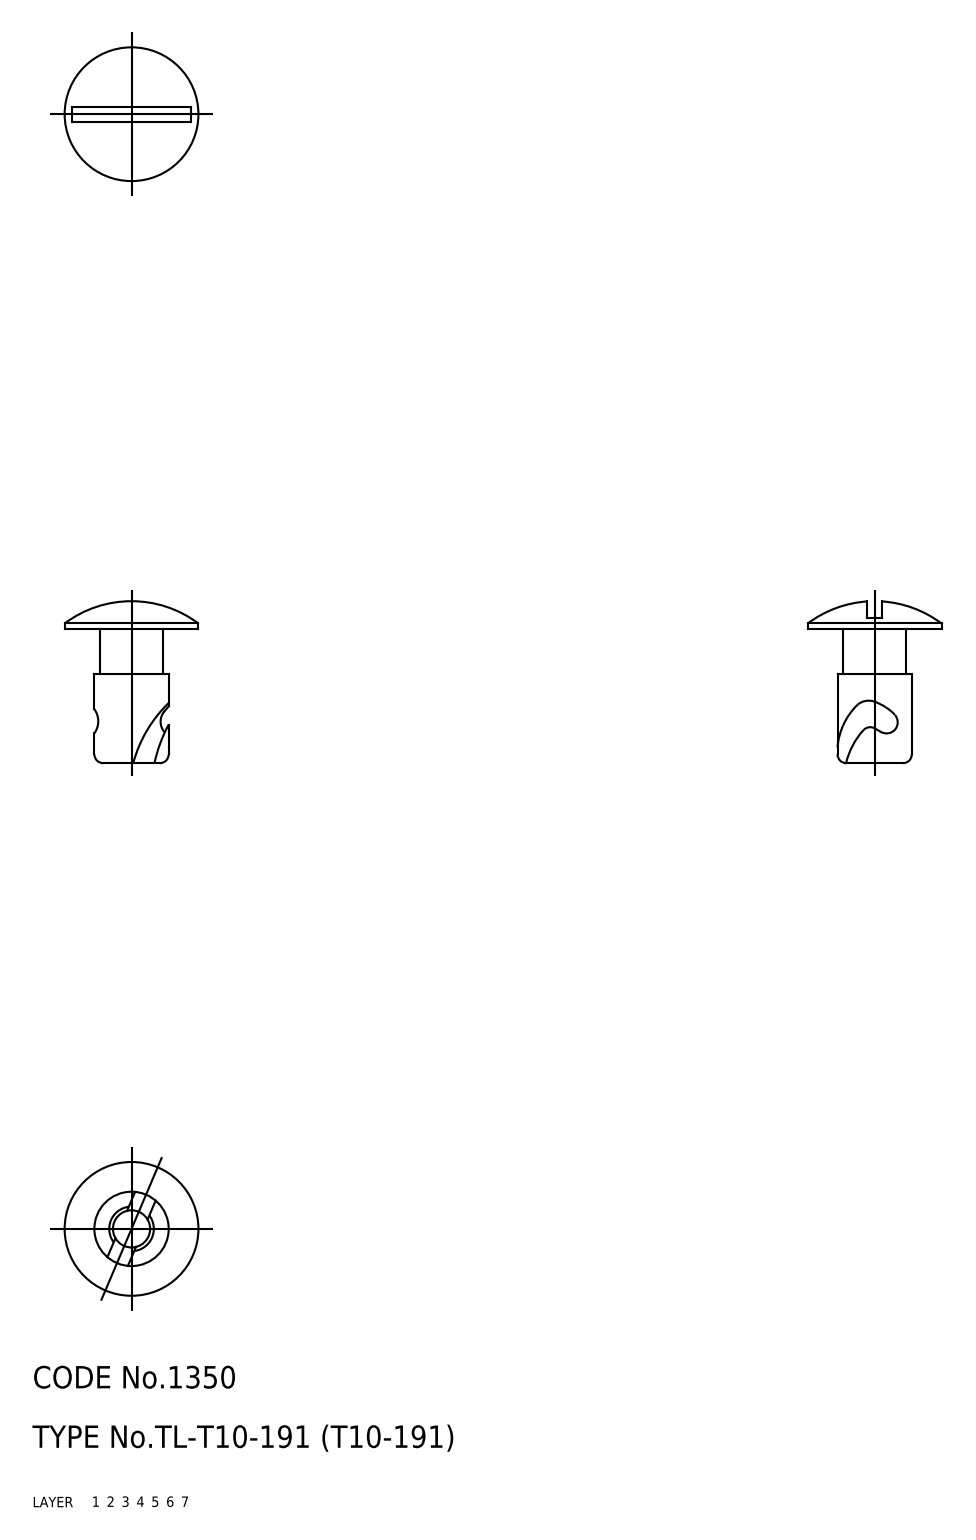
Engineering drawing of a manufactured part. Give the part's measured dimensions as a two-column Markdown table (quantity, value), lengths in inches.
| quantity | value |
| --- | --- |
| part name | fastener |
| STEP written by | CADfix (AUTOMOTIVE_DESIGN) |
| units | inches |
| bodies | 1 solid, 36 faces (0 planar, 0 cylindrical, 36 other) |
| overall size | 0.857 × 0.709 × 0.709 |
| volume | 0.091 in³ |
| surface area | 2.055 in² |
